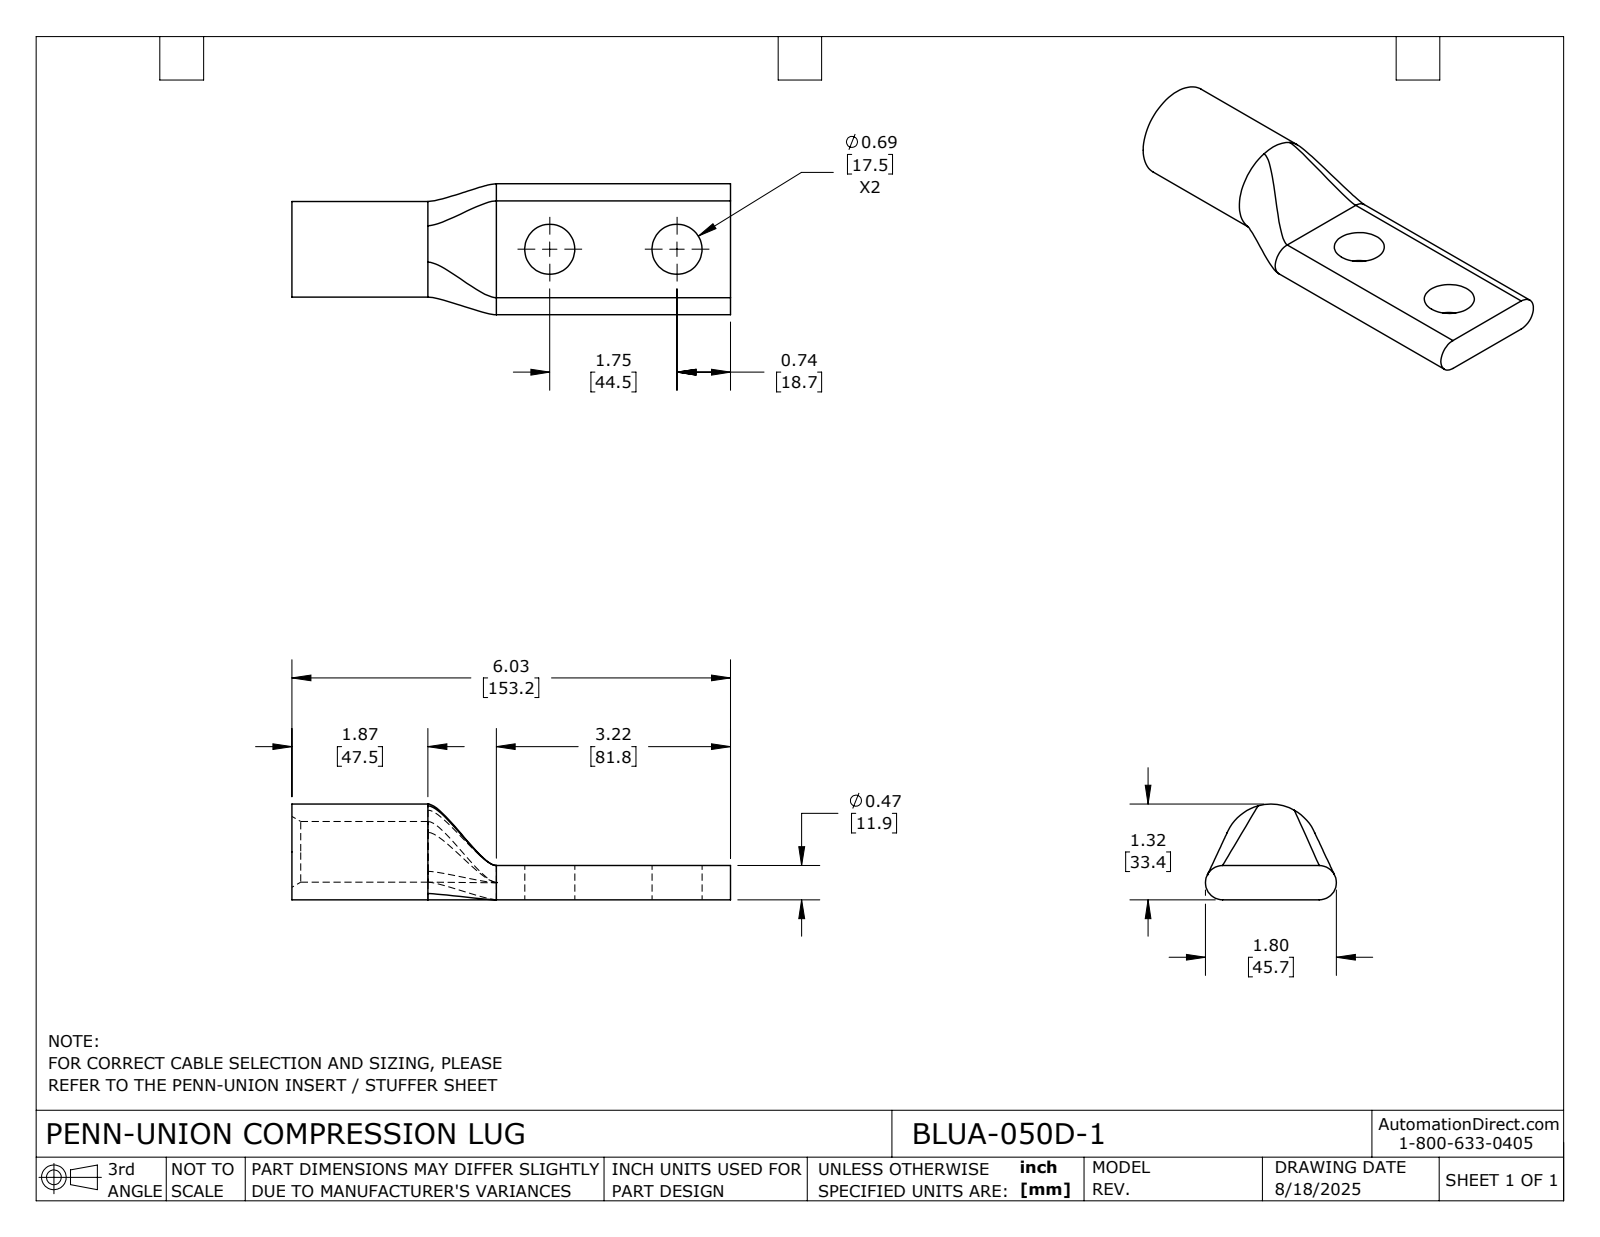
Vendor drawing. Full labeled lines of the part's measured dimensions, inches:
Part name (STEP PRODUCT): BLUA-050D-1
STEP written by: SolidWorks 2024 (CONFIG_CONTROL_DESIGN)
Units: inches
Bodies: 1 solid, 26 faces (5 planar, 11 cylindrical, 10 other)
Overall size (bounding box): 6.03 × 1.8 × 1.315
Volume: 4.48 in³ · Surface area: 35.02 in²
Round holes (diameter × count): ⌀0.688 ×2, ⌀0.834 ×1
Round bosses / shafts (diameter × count): ⌀1.315 ×1
Partial cylindrical surfaces — rounded edges, fillets, slot ends (radius × count): R0.235 ×2
Main face-to-face distances: 0.47, 6.03, 2.81, 3.22
Hole centre spacings: 1.75
